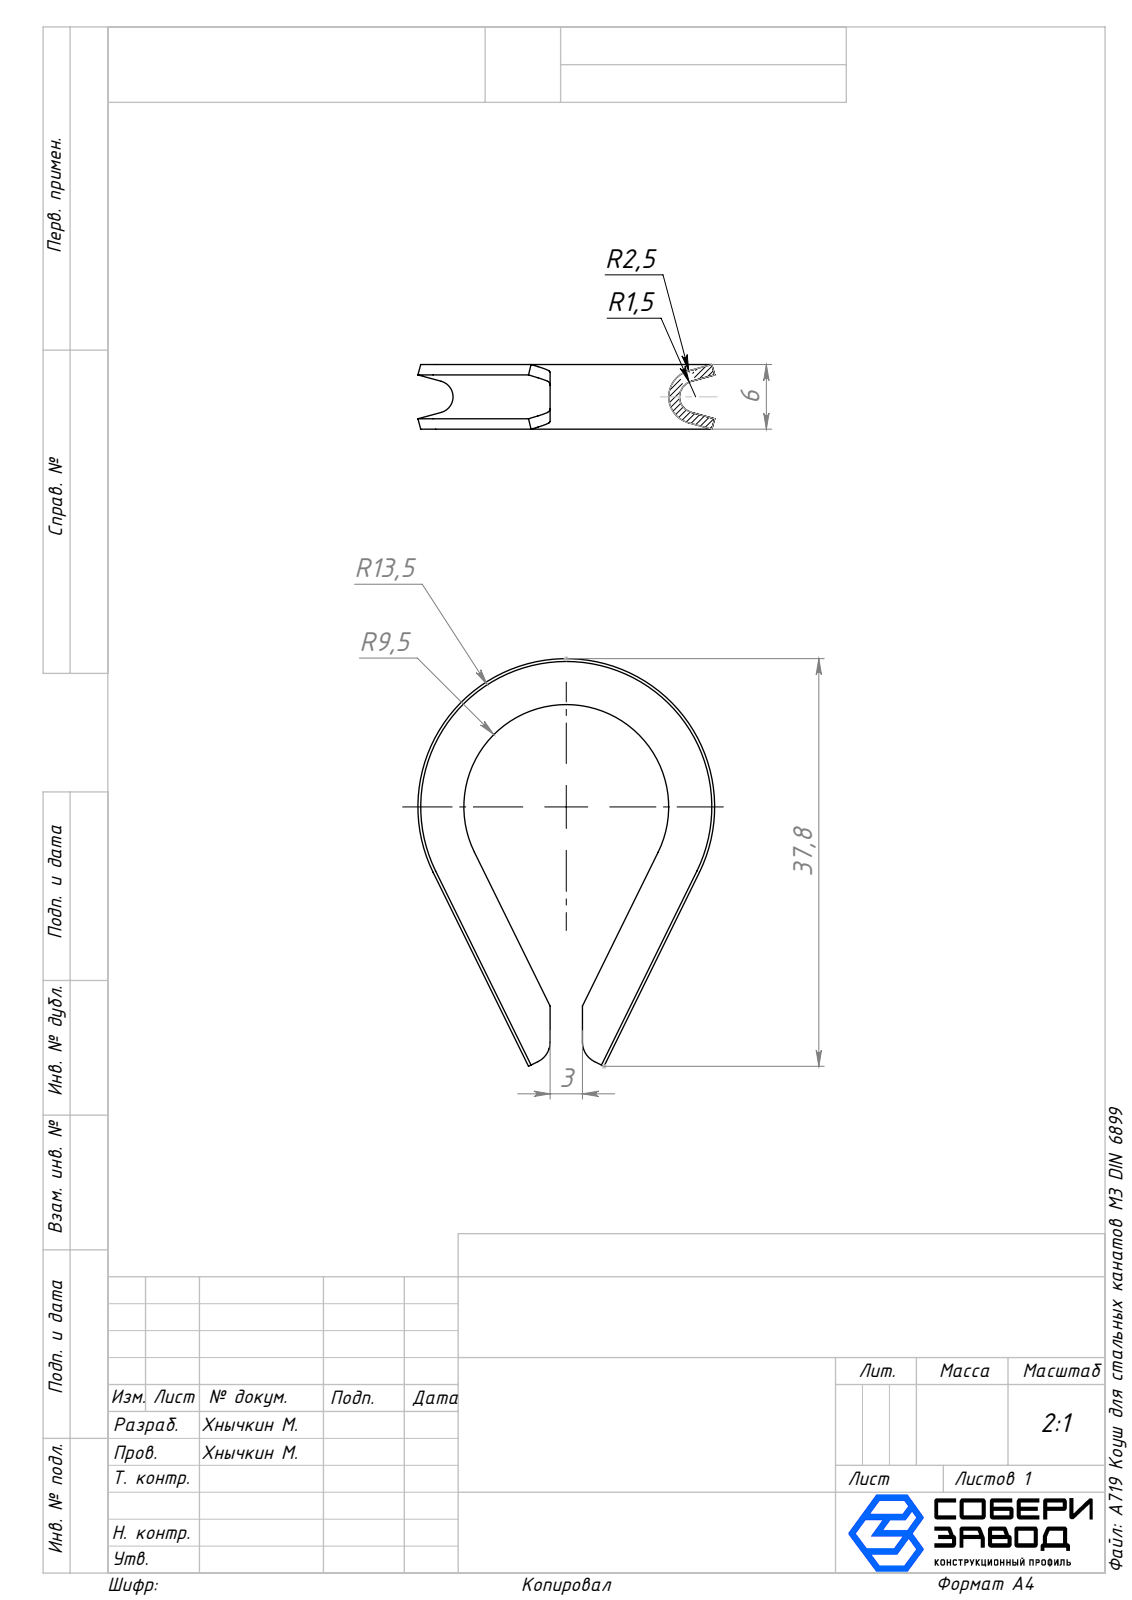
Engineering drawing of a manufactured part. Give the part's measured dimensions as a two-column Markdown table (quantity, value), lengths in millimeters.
| quantity | value |
| --- | --- |
| part name | A719 Коуш для стальных канатов М3 DIN 6899 |
| STEP written by | SolidWorks 2025 (AUTOMOTIVE_DESIGN) |
| units | millimeters |
| bodies | 1 solid, 43 faces (18 planar, 12 cylindrical, 13 other) |
| overall size | 37.84 × 27.53 × 6 |
| volume | 815 mm³ |
| surface area | 1 848 mm² |
| partial cylindrical surfaces (radius × count) | 1.5 × 2, 2 × 2, 2.5 × 2 |
| main face-to-face distances | 1, 3 |
